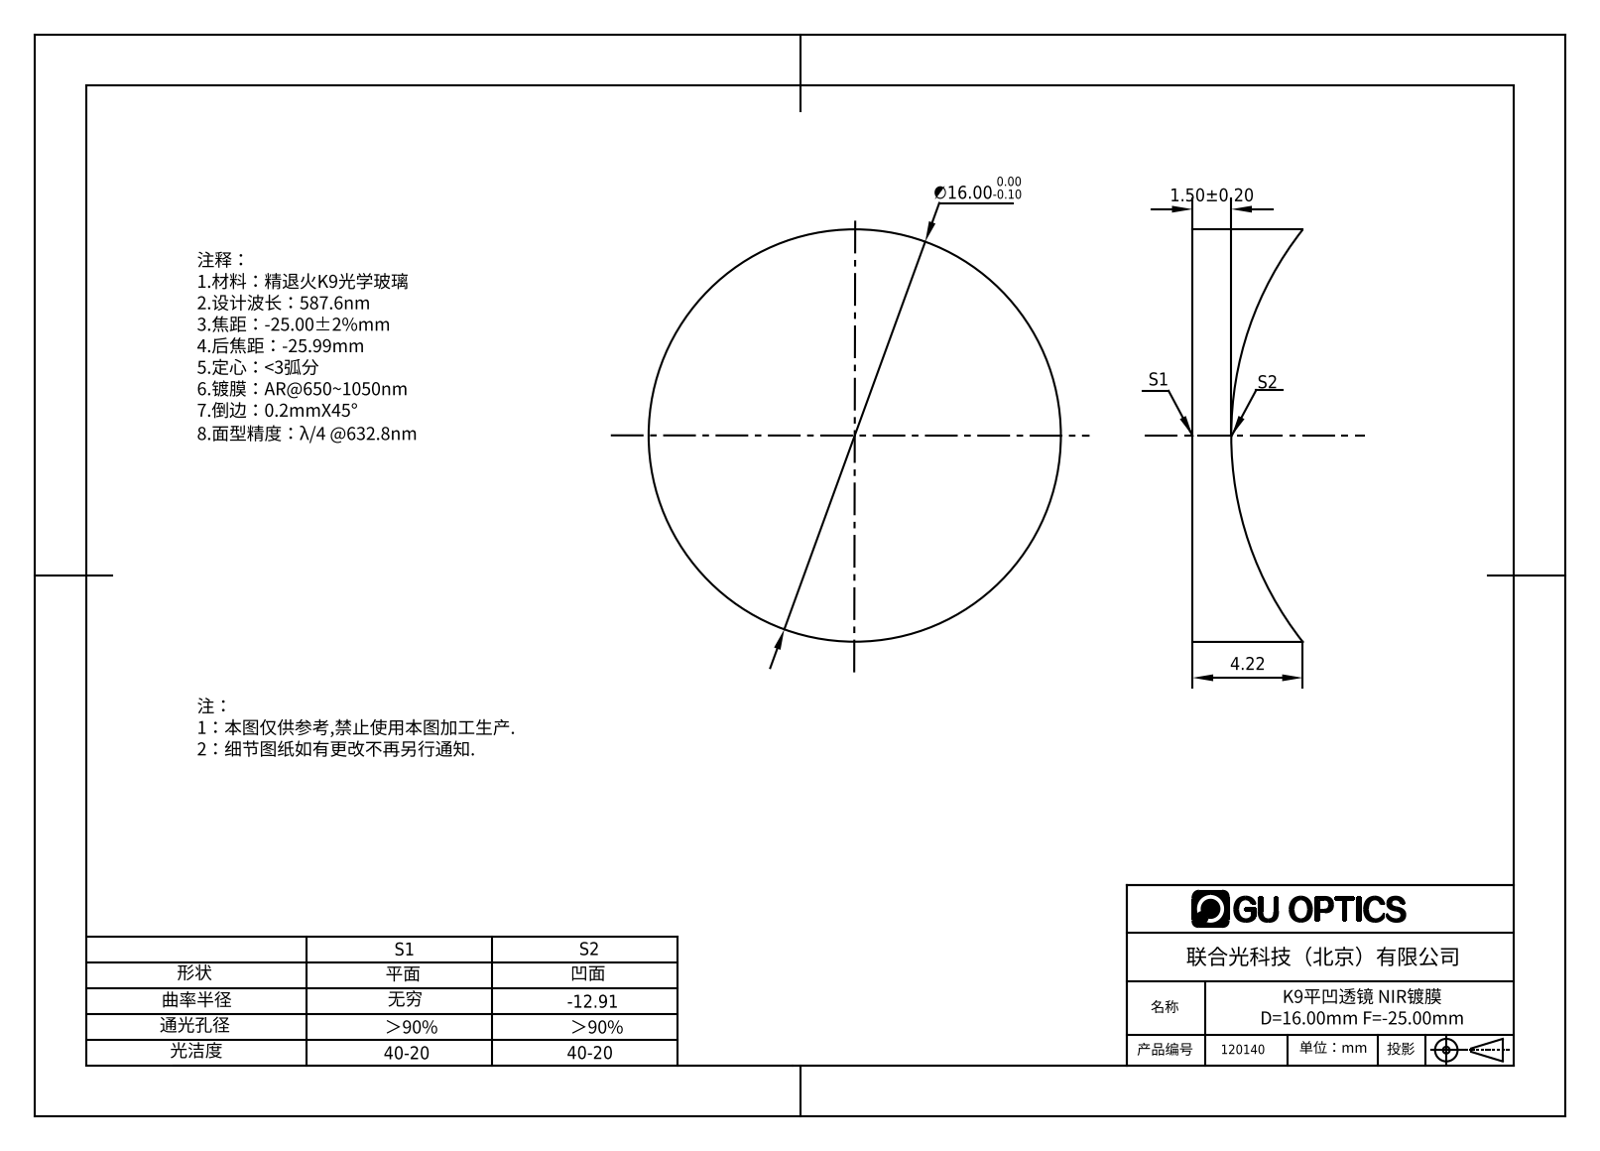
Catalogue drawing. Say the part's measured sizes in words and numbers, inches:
The part is named "120140". Its 3-D file was written by "SolidWorks 2016 (AUTOMOTIVE_DESIGN)". It is 1 solid with 5 faces: 1 planar, 2 cylindrical and 2 other. Overall it measures 0.63 by 0.63 by 0.169 inches. Its volume is 0.035 cubic inches and its surface area 0.994 square inches. Round bosses or shafts: 1 of diameter 0.63.
